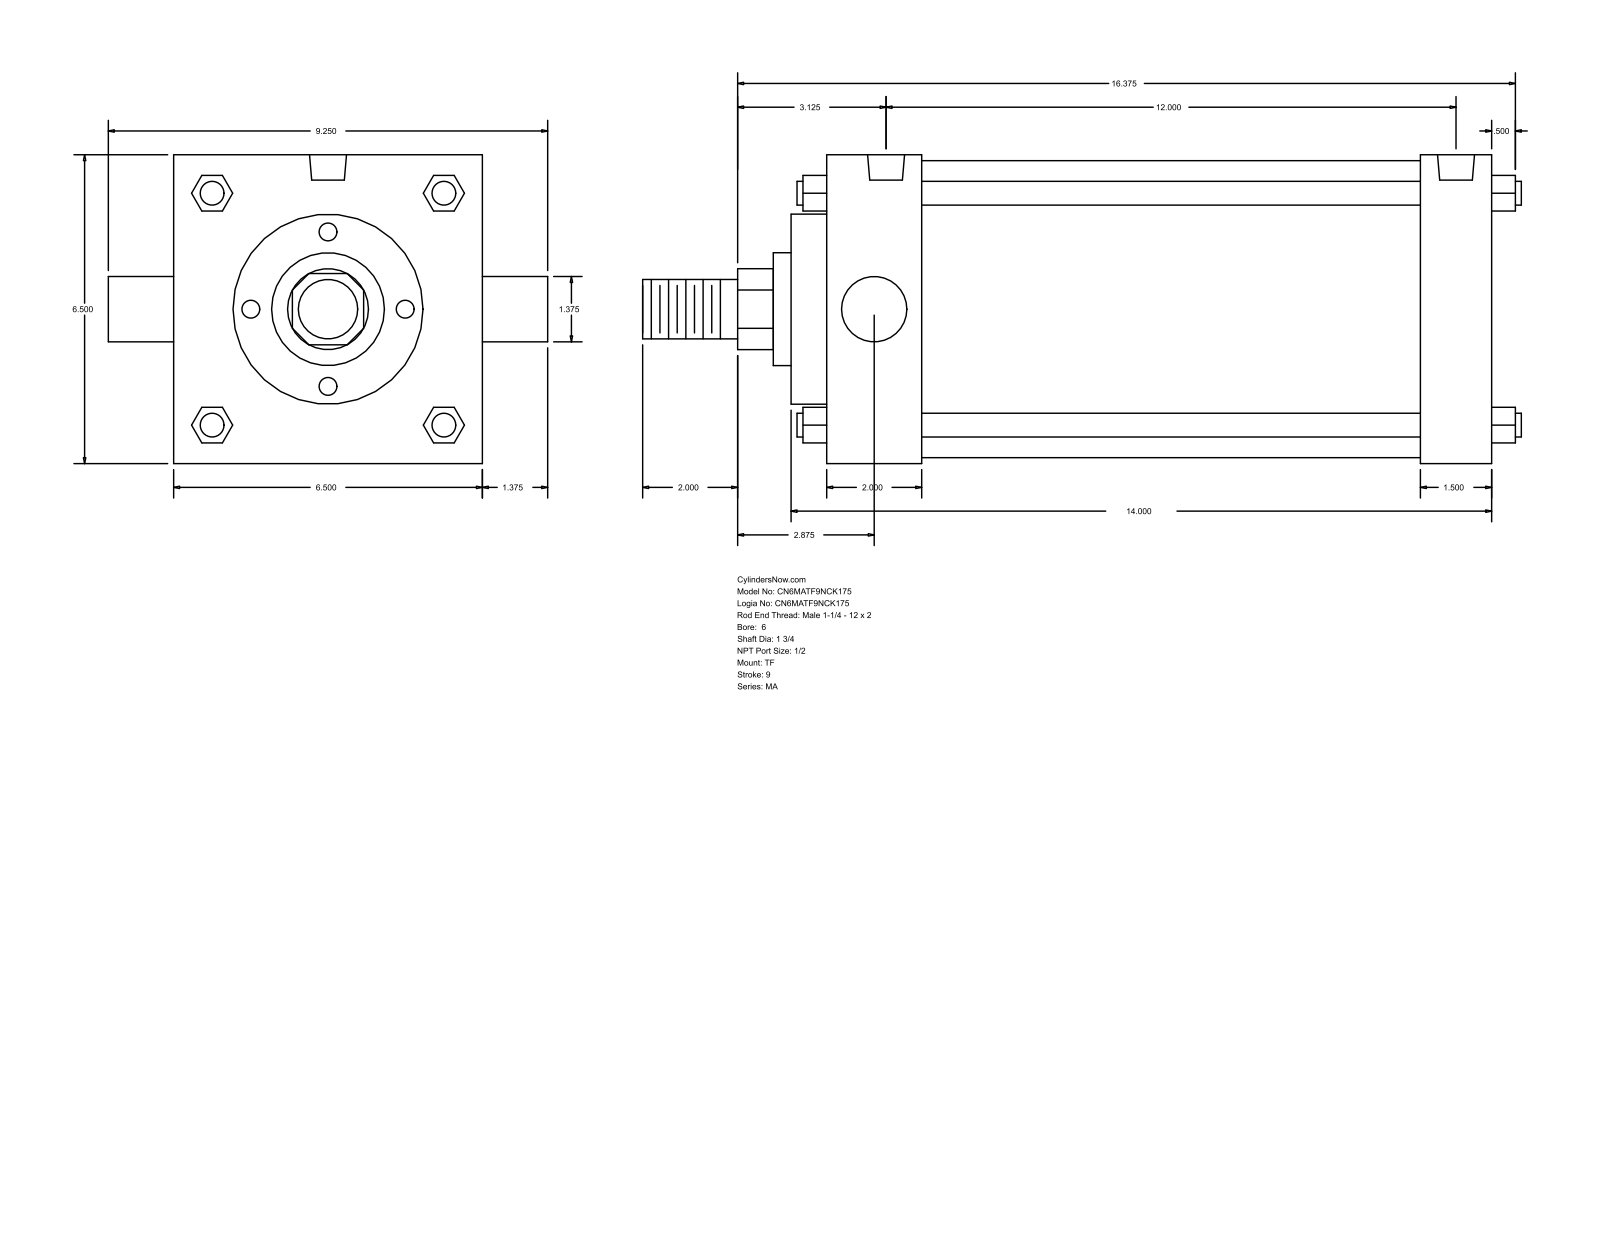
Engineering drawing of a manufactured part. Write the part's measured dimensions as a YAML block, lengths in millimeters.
part_name: "MA_TF__0600_1.75"
step_written_by: "GSSL Pune (CONFIG_CONTROL_DESIGN)"
units: millimeters
bodies: {solids: 0, faces: 122, planar: 93, cylindrical: 29, other: 0}
overall_size: [469.9, 234.95, 165.1]
round_holes:
  - {diameter: 17.46, count: 3}
  - {diameter: 19.77, count: 2}
round_bosses_or_shafts:
  - {diameter: 12.7, count: 4}
  - {diameter: 158.75, count: 1}
  - {diameter: 101.6, count: 1}
  - {diameter: 60.33, count: 1}
  - {diameter: 44.45, count: 1}
  - {diameter: 34.92, count: 1}
  - {diameter: 31.75, count: 1}
partial_cylinders:
  - {radius: 21.63, count: 1}
face_to_face_distances: [165.1, 355.61, 19.05, 50.8, 304.81, 317.5, 266.7, 38.11, 69.85, 336.55]
hole_center_spacings: [304.8]
